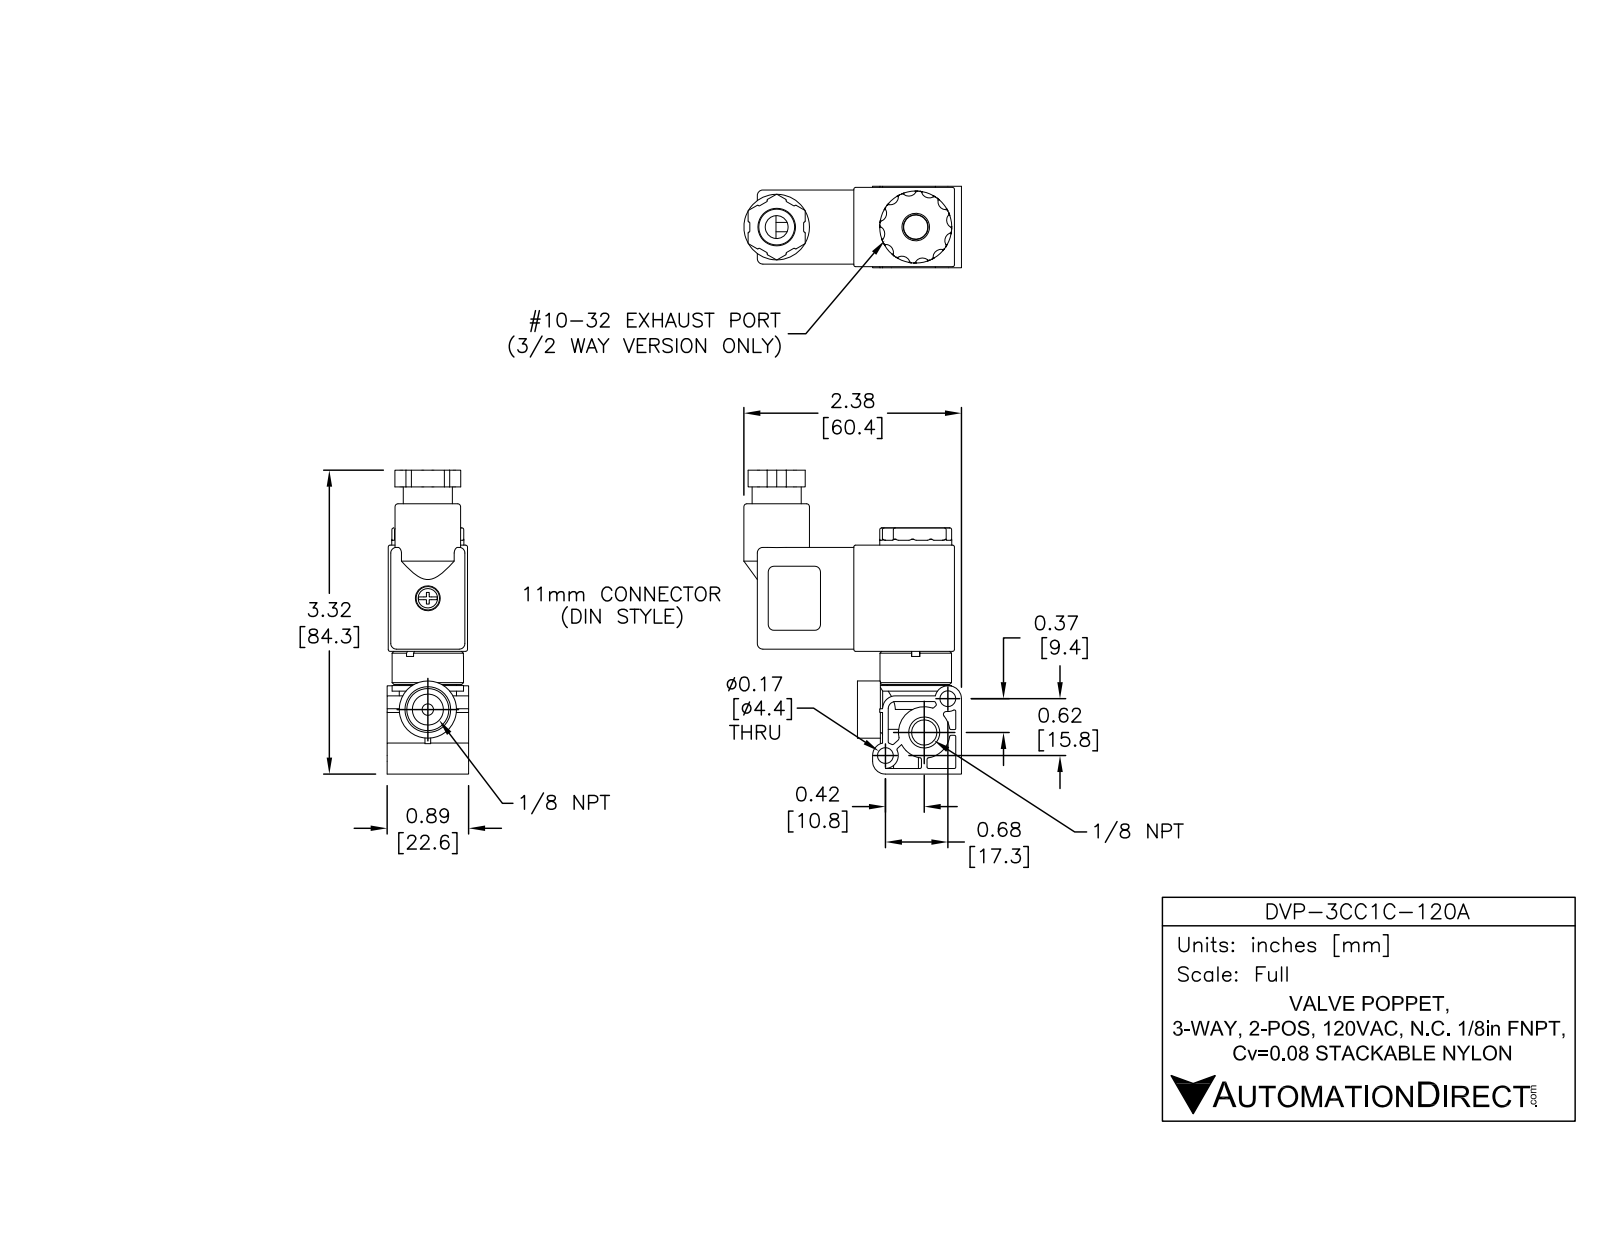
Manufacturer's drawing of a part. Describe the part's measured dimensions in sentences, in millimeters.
The part is named "DVP-3CC1C-120A". Its 3-D file was written by "SolidWorks 2015 (AUTOMOTIVE_DESIGN)". It is 5 solids with 1465 faces: 664 planar, 318 cylindrical and 483 other. Overall it measures 84 by 60.4 by 22.6 millimeters. Its volume is 34 870 cubic millimeters and its surface area 25 320 square millimeters. Round holes: 2 of diameter 2.5, 2 of diameter 3.2, 2 of diameter 3.8, 2 of diameter 4.4, 2 of diameter 8.6, 1 of diameter 1.4, 1 of diameter 2.3, 1 of diameter 2.6, 1 of diameter 4.2, 1 of diameter 5, 1 of diameter 6.4, 1 of diameter 6.8. Round bosses or shafts: 2 of diameter 15.9, 1 of diameter 20, 1 of diameter 19.8, 1 of diameter 18.2, 1 of diameter 16.6, 1 of diameter 14.5, 1 of diameter 13.6, 1 of diameter 13.3. Partial cylindrical surfaces (rounded edges, fillets, slot ends): 28 of radius 0.4, 25 of radius 0.3, 24 of radius 0.6, 12 of radius 0.5, 12 of radius 1.6, 12 of radius 2.2, 5 of radius 0.8, 4 of radius 3.6. The main face-to-face distances are 2, 20, 1.3, 20.3, 19.3, 0.7, 21.3, 22, 18, 22.3. The hole center spacings are 8.3, 10.7, 11.4, 12.5, 13.3, 18.6, 23.4, 24.
